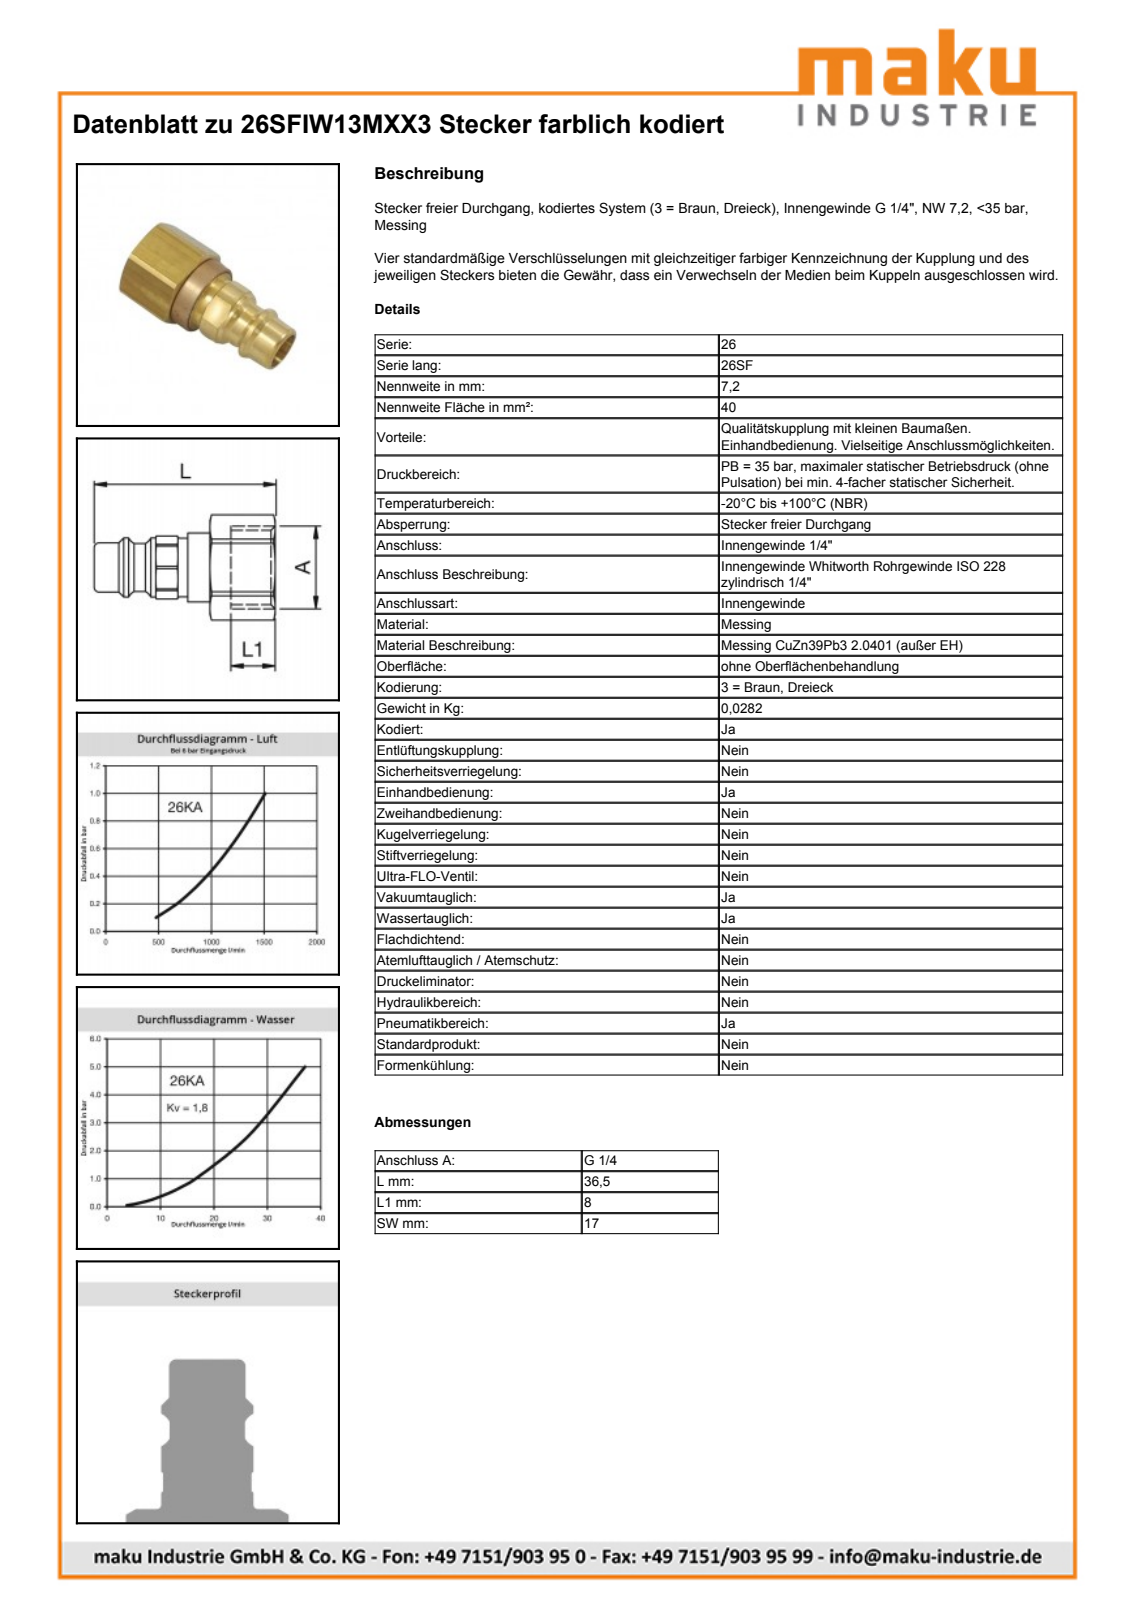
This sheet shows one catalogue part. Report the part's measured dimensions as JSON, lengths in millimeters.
{"part_name": "D112679; D112675; D103012", "step_written_by": "Autodesk Inventor 2013 (AUTOMOTIVE_DESIGN)", "units": "millimeters", "bodies": {"solids": 2, "faces": 61, "planar": 16, "cylindrical": 20, "other": 25}, "overall_size": [36.5, 19.15, 17], "volume_mm3": 3659, "surface_area_mm2": 3492, "round_holes": [[7.85, 1], [11.45, 1], [13.85, 1], [14.05, 1]], "round_bosses_or_shafts": [[15.5, 1], [14, 1], [12, 1], [11.9, 1], [10, 1], [9.75, 1]], "partial_cylinders_radius": [[6.6, 1], [9.57, 1]], "face_to_face_distances": [17, 13, 4.5, 17.5, 7.5, 3, 10, 14.8, 2.2, 4.2]}
